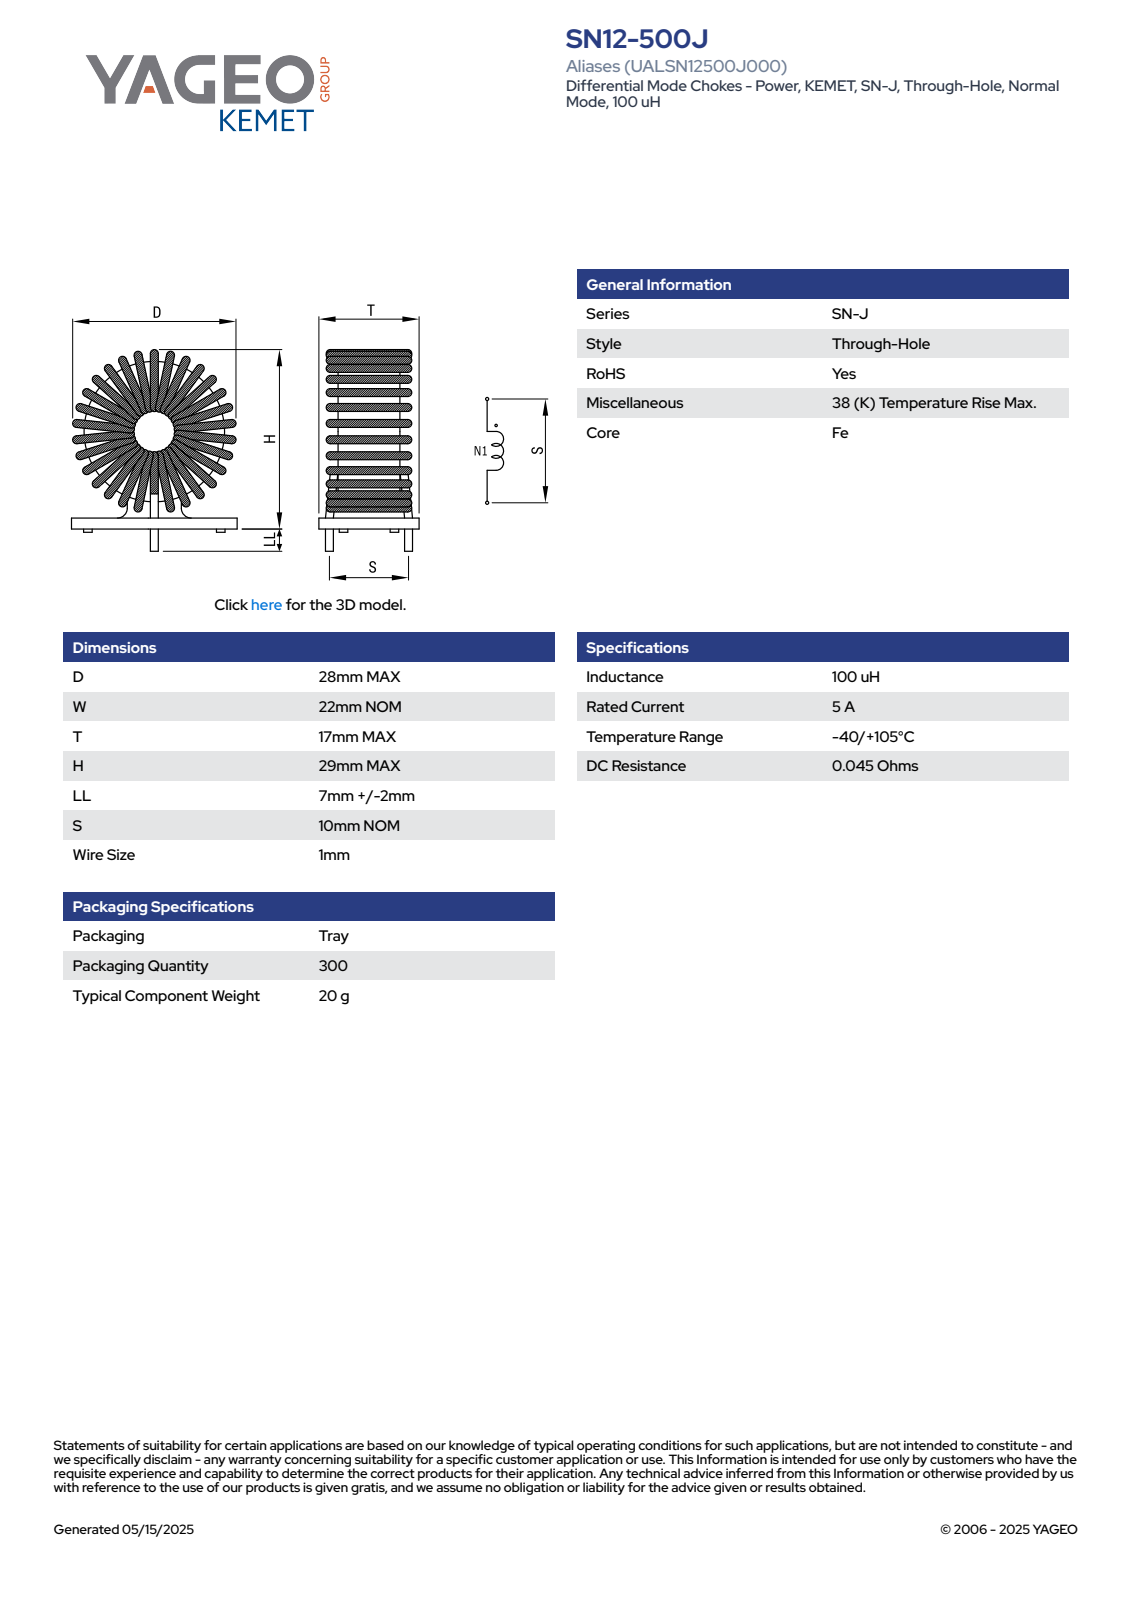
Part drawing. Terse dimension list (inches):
name: SN12-500J
written by: SolidWorks 2018 (AUTOMOTIVE_DESIGN)
unit: in
bodies: 1 solid, 134 faces (44 planar, 45 cylindrical, 45 other)
size: 1.417 × 1.102 × 0.669
volume: 0.505 in³; area: 5.741 in²
holes: 1× ⌀0.409
bosses: 3× ⌀0.039
rounds: 10× R0.02, 1× R0.226, 1× R0.246, 1× R0.407, 1× R0.427, 1× R0.551, 1× R0.551
face distances: 0.669, 0.179, 0.49, 0.059, 0.098, 0.571, 0.081, 0.392, 0.311, 0.02
